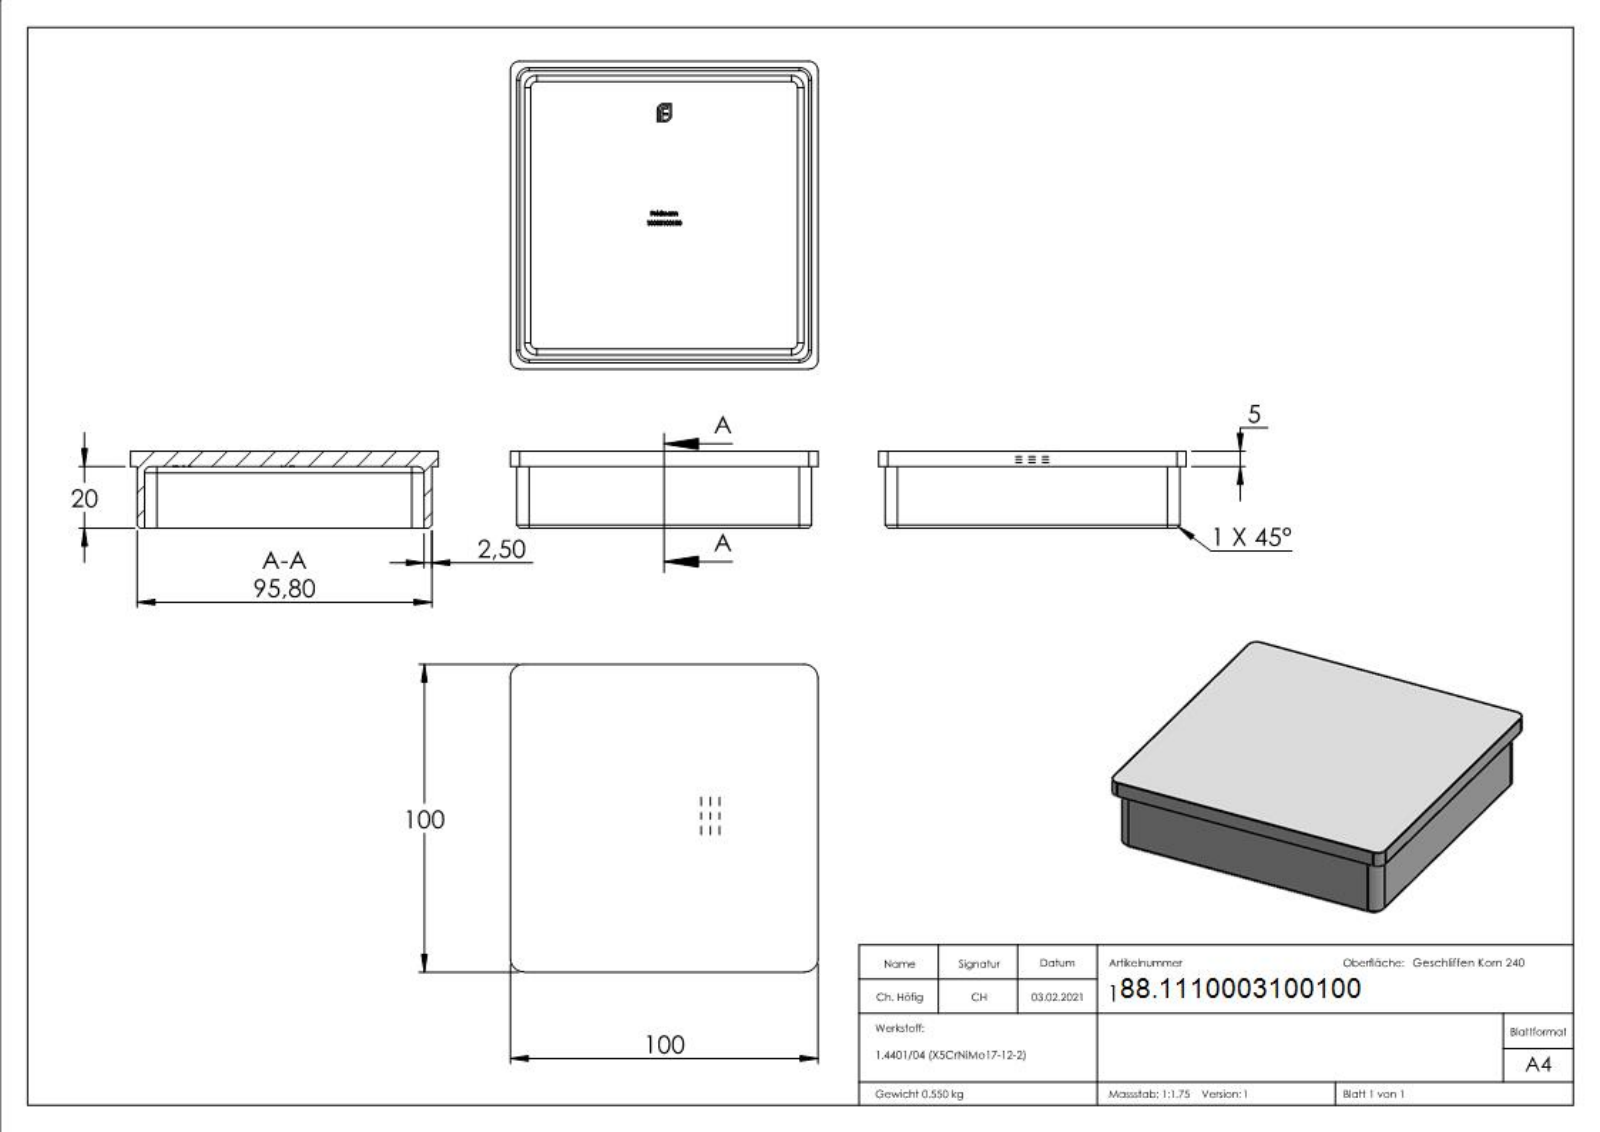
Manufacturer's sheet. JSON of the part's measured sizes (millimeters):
{"part_name": "10003100100", "step_written_by": "SolidWorks 2018 (CONFIG_CONTROL_DESIGN)", "units": "millimeters", "bodies": {"solids": 1, "faces": 314, "planar": 145, "cylindrical": 16, "other": 153}, "overall_size": [100, 100, 25], "volume_mm3": 68736, "surface_area_mm2": 36099, "partial_cylinders_radius": [[4, 8], [2, 4], [3, 4]], "face_to_face_distances": [5, 2.5, 93.3, 95.8, 90.8, 2.1, 4.6, 95.4, 97.9, 100]}
